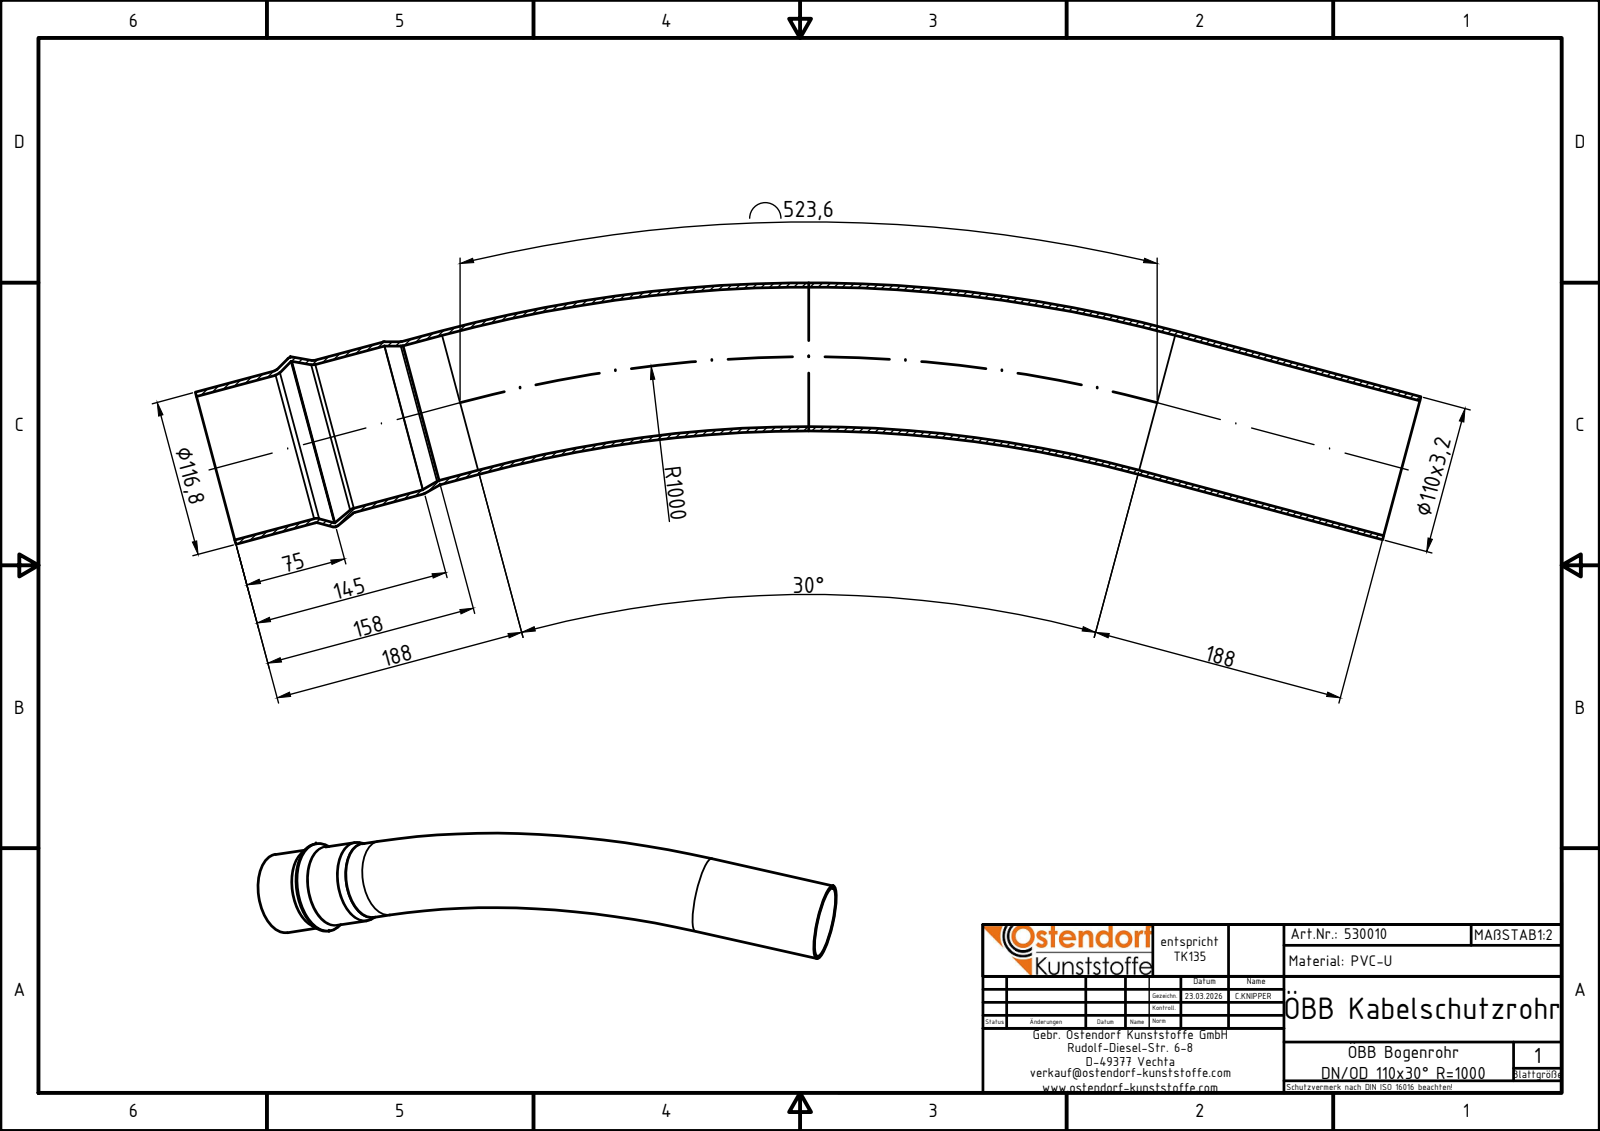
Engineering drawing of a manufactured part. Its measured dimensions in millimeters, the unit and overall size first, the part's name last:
Units: millimetres
Overall size (bounding box): 878.31 × 340.86 × 130.5
Round holes (diameter × count): ⌀103.59 ×2, ⌀110.4 ×1, ⌀124.1 ×1
Round bosses / shafts (diameter × count): ⌀110 ×2, ⌀130.5 ×1, ⌀116.8 ×1
Volume: 983 362 mm³ · Surface area: 616 306 mm²
Bodies: 1 solid, 32 faces (2 planar, 10 cylindrical, 20 other)
Part name (STEP PRODUCT): 530010z
STEP written by: Autodesk Inventor 2024 (AUTOMOTIVE_DESIGN)
